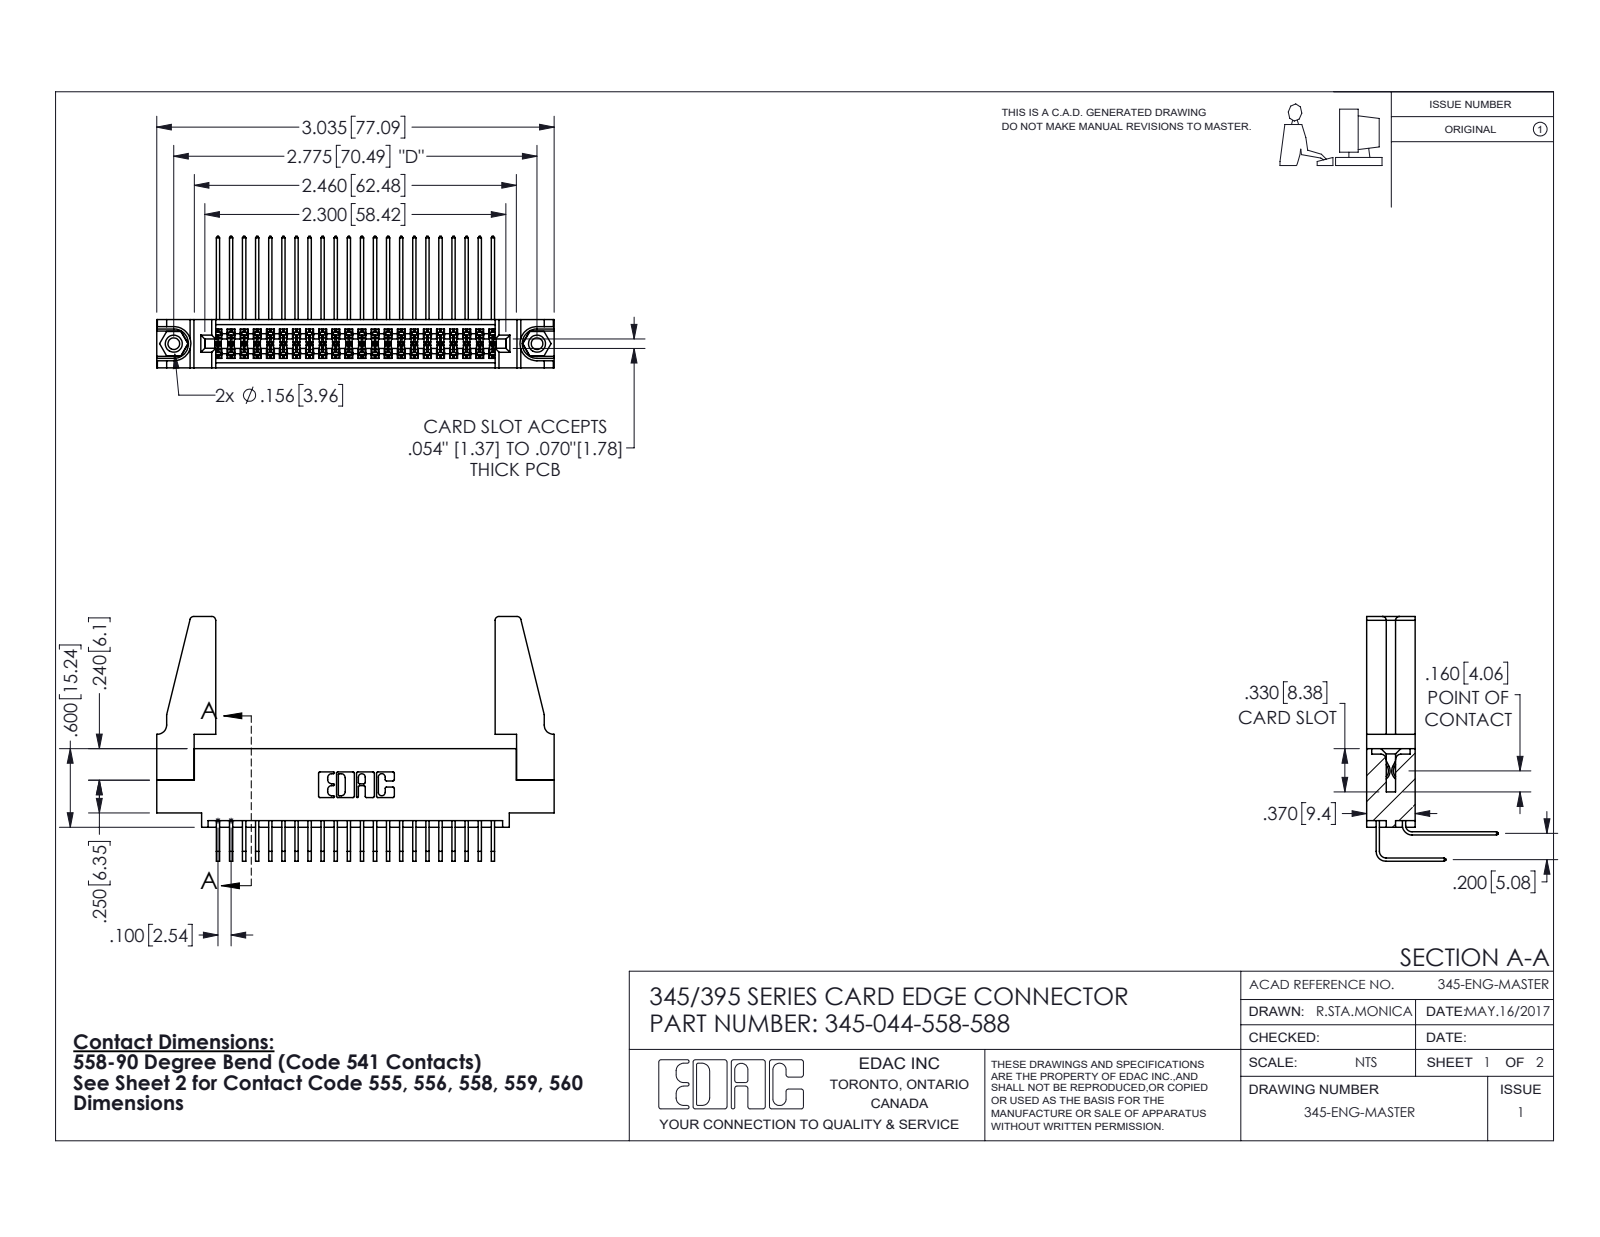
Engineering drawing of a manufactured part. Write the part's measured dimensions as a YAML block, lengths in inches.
part_name: "345-220-078_345-220-088; 345 Part_0.110 Offset - 0.156 Dia-TH; 345-250-001_345-250-001-102; 345-292-001_558 559 Tail - 1 (+2 more)"
step_written_by: "SolidWorks 2016 (CONFIG_CONTROL_DESIGN)"
units: inches
bodies: {solids: 49, faces: 2542, planar: 1696, cylindrical: 830, other: 16}
overall_size: [3.036, 1.869, 1.005]
volume: 0.655
surface_area: 23.38
round_holes:
  - {diameter: 0.089, count: 2}
  - {diameter: 0.125, count: 2}
  - {diameter: 0.156, count: 2}
  - {diameter: 0.064, count: 1}
round_bosses_or_shafts:
  - {diameter: 0.155, count: 2}
partial_cylinders:
  - {radius: 0.006, count: 88}
  - {radius: 0.01, count: 22}
  - {radius: 0.03, count: 8}
  - {radius: 0.007, count: 6}
  - {radius: 0.031, count: 6}
  - {radius: 0.026, count: 3}
  - {radius: 0.014, count: 2}
  - {radius: 0.019, count: 2}
face_to_face_distances: [0.072, 0.298, 0.37, 0.2, 0.098, 0.272, 0.025, 0.225, 0.025, 0.175]
hole_center_spacings: [0.27, 2.541, 2.775]
